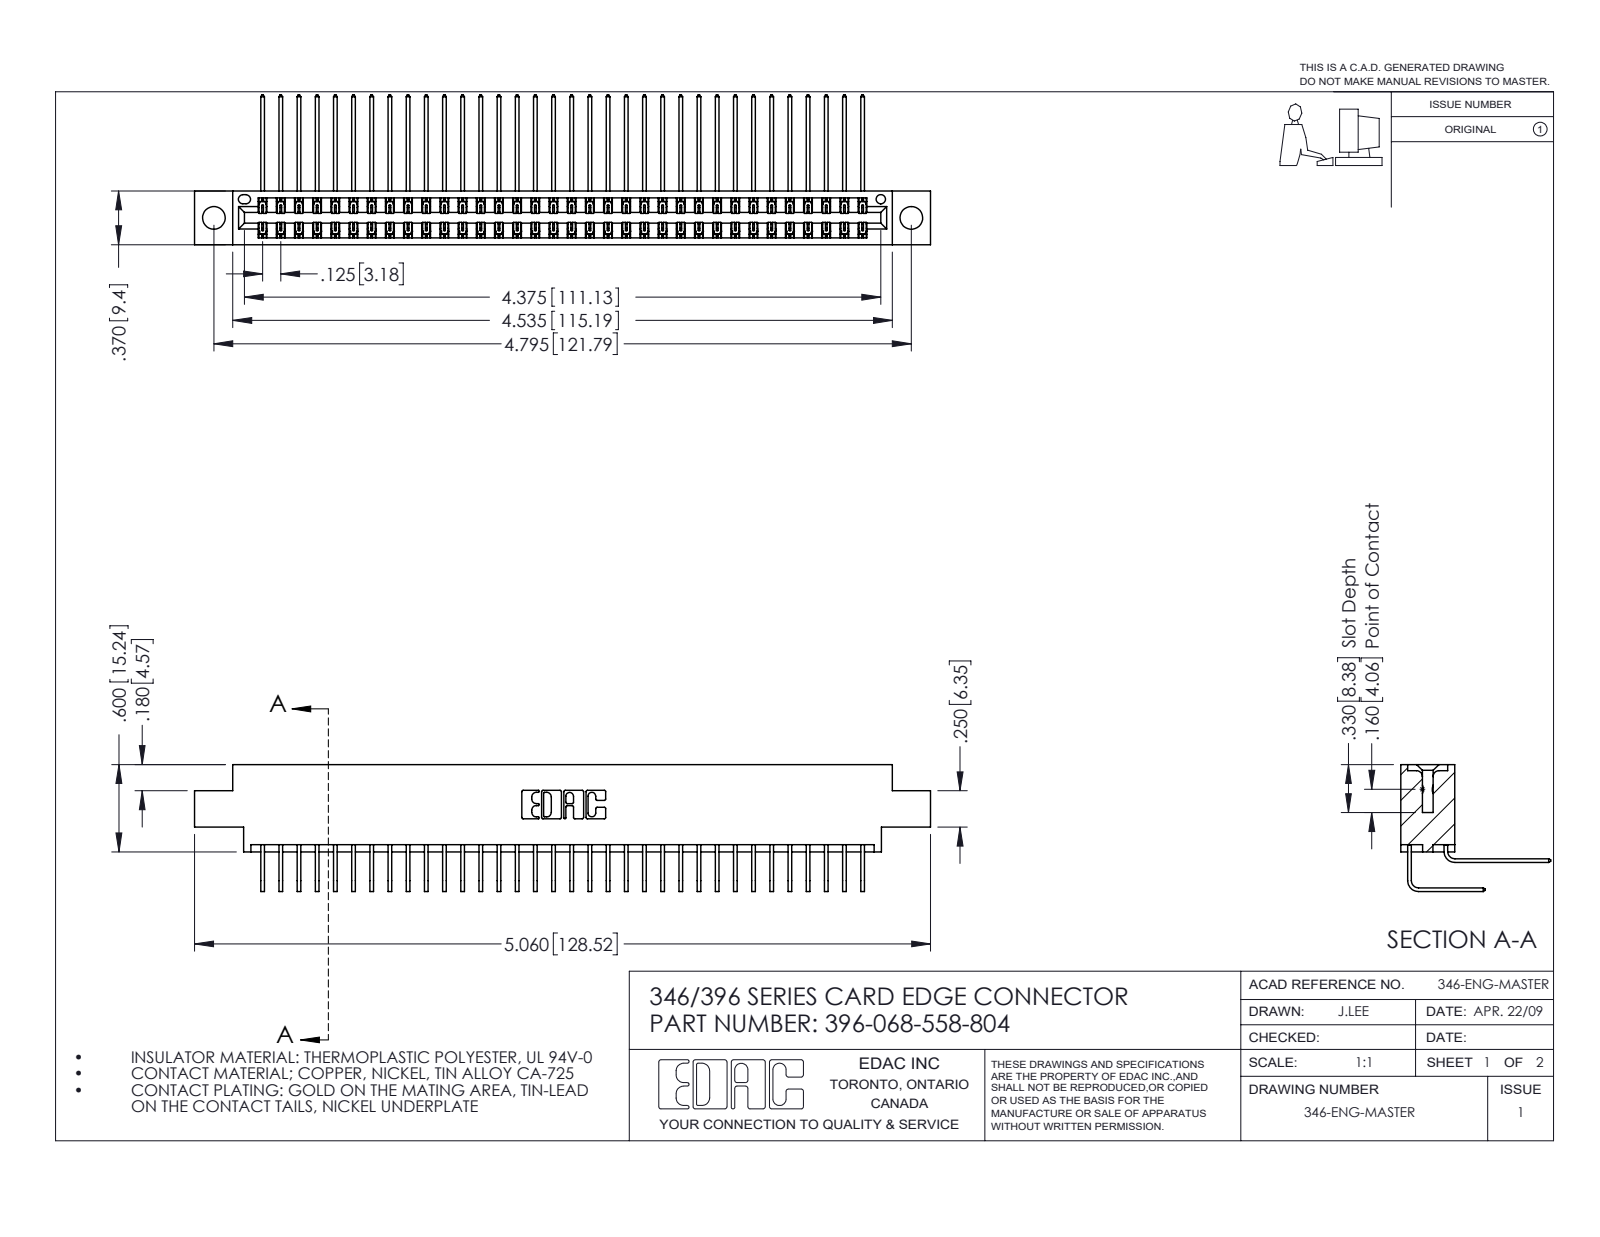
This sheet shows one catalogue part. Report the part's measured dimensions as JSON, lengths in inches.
{"part_name": "396-068-558-804; 345-292-001_558 Tail - 2; 345-292-001_558 559 Tail - 1; 346 Part_0.170 Offset - 0.156 Dia-TH", "step_written_by": "SolidWorks 2016 (CONFIG_CONTROL_DESIGN)", "units": "inches", "bodies": {"solids": 69, "faces": 3798, "planar": 2596, "cylindrical": 1202, "other": 0}, "overall_size": [5.06, 1.03, 0.873], "volume_in3": 0.77, "surface_area_in2": 29.6, "round_holes": [[0.156, 2], [0.064, 1]], "partial_cylinders_radius": [[0.006, 102], [0.01, 22], [0.007, 6], [0.031, 6], [0.026, 3], [0.014, 2], [0.022, 2], [0.024, 2]], "face_to_face_distances": [0.322, 0.048, 0.025, 0.37, 0.25, 0.298, 0.072, 0.275, 0.148, 0.222], "hole_center_spacings": [0.246, 4.587, 4.795]}
